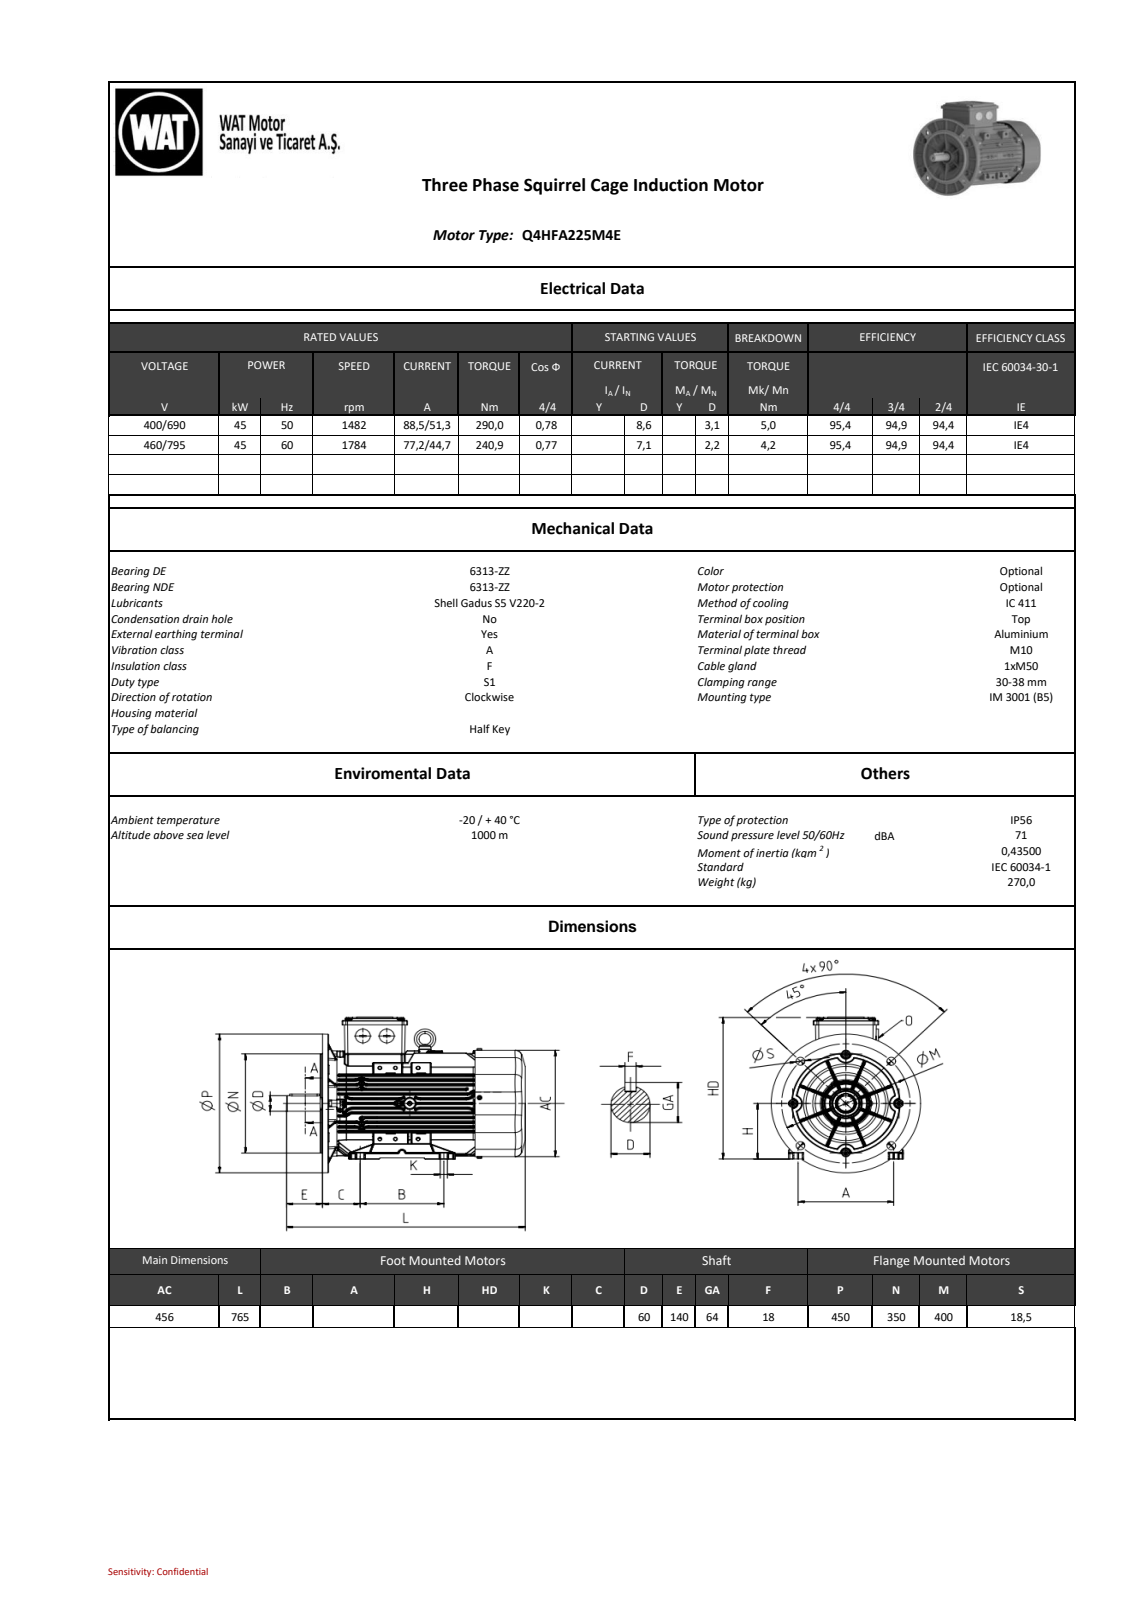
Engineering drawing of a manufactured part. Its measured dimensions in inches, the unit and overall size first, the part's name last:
Units: inches
Overall size (bounding box): 30.118 × 19.98 × 17.717
Round holes (diameter × count): ⌀0.748 ×8, ⌀0.028 ×6, ⌀0.236 ×5, ⌀0.295 ×5, ⌀0.169 ×4, ⌀0.217 ×4, ⌀0.256 ×4, ⌀0.33 ×4, ⌀0.413 ×4, ⌀0.768 ×4, ⌀0.157 ×3, ⌀0.197 ×3
Round bosses / shafts (diameter × count): ⌀0.394 ×6, ⌀0.65 ×4, ⌀0.63 ×4, ⌀0.23 ×3, ⌀2.283 ×2, ⌀2.169 ×2, ⌀2.059 ×2, ⌀2.055 ×2
Partial cylindrical surfaces — rounded edges, fillets, slot ends (radius × count): R0.039 ×619, R0.079 ×408, R0.008 ×332, R0.02 ×154, R0.197 ×81, R0.098 ×76, R0.118 ×48, R0.157 ×48
Main face-to-face distances: 7.473, 0.611, 6.655, 0.818, 0.584, 0.206, 7.267, 0.97, 5.915, 1.558
Hole centre spacings: 0.291, 6.142, 5.761, 11.136, 2.684, 3.255, 7.874, 9.115
Bodies: 0 solids, 14199 faces (6159 planar, 2712 cylindrical, 5328 other)
Part name (STEP PRODUCT): AB_objects
STEP written by: SIEMENS PLM Software NX2206.8101 (AUTOMOTIVE_DESIGN)
